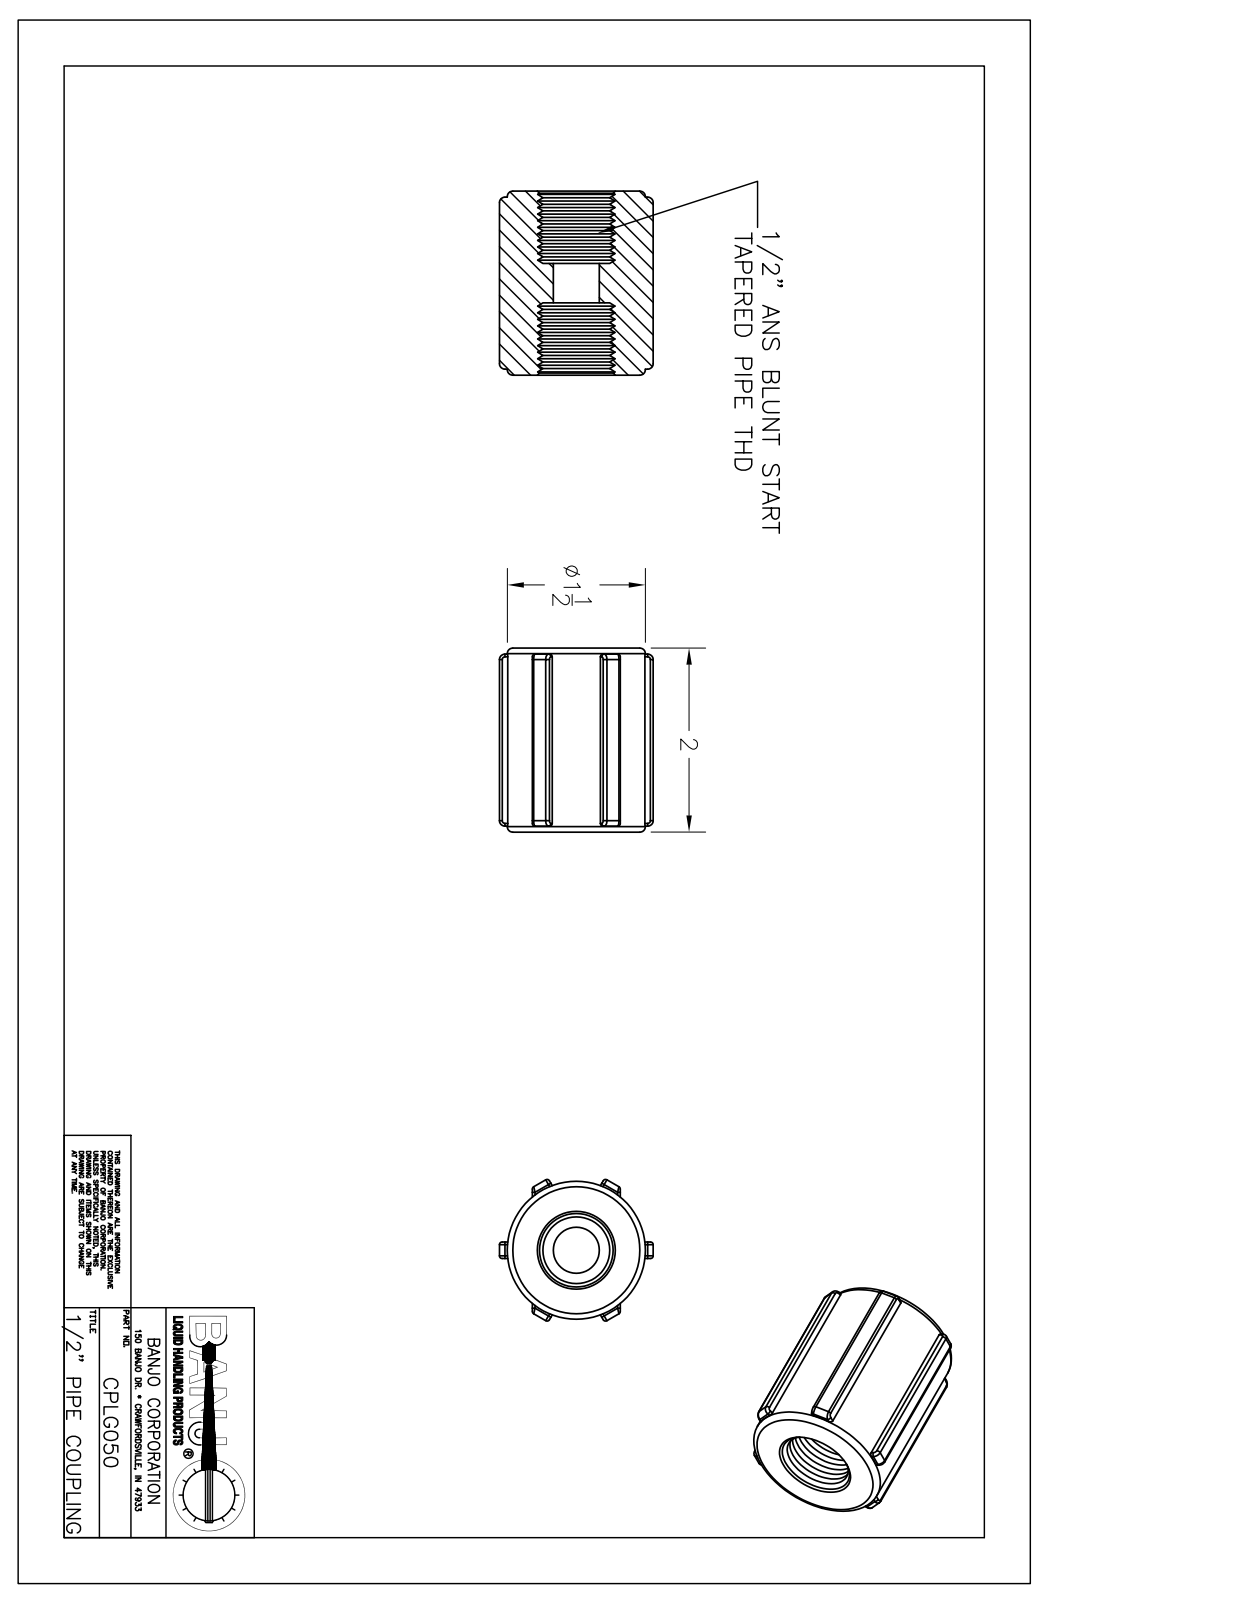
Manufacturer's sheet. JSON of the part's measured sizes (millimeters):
{"part_name": "CPLG050", "step_written_by": "Autodesk Inventor 2012 (AUTOMOTIVE_DESIGN)", "units": "millimeters", "bodies": {"solids": 1, "faces": 549, "planar": 183, "cylindrical": 70, "other": 296}, "overall_size": [50.8, 42.7, 39.6], "volume_mm3": 48440, "surface_area_mm2": 13880, "round_holes": [[12.7, 1], [18.4, 1]], "partial_cylinders_radius": [[0.8, 24], [18.8, 1], [19.1, 1]], "face_to_face_distances": [42.7, 50.8, 7.9, 34.8, 20.1, 30.7, 26.8, 6.4, 10.7, 1.1]}
